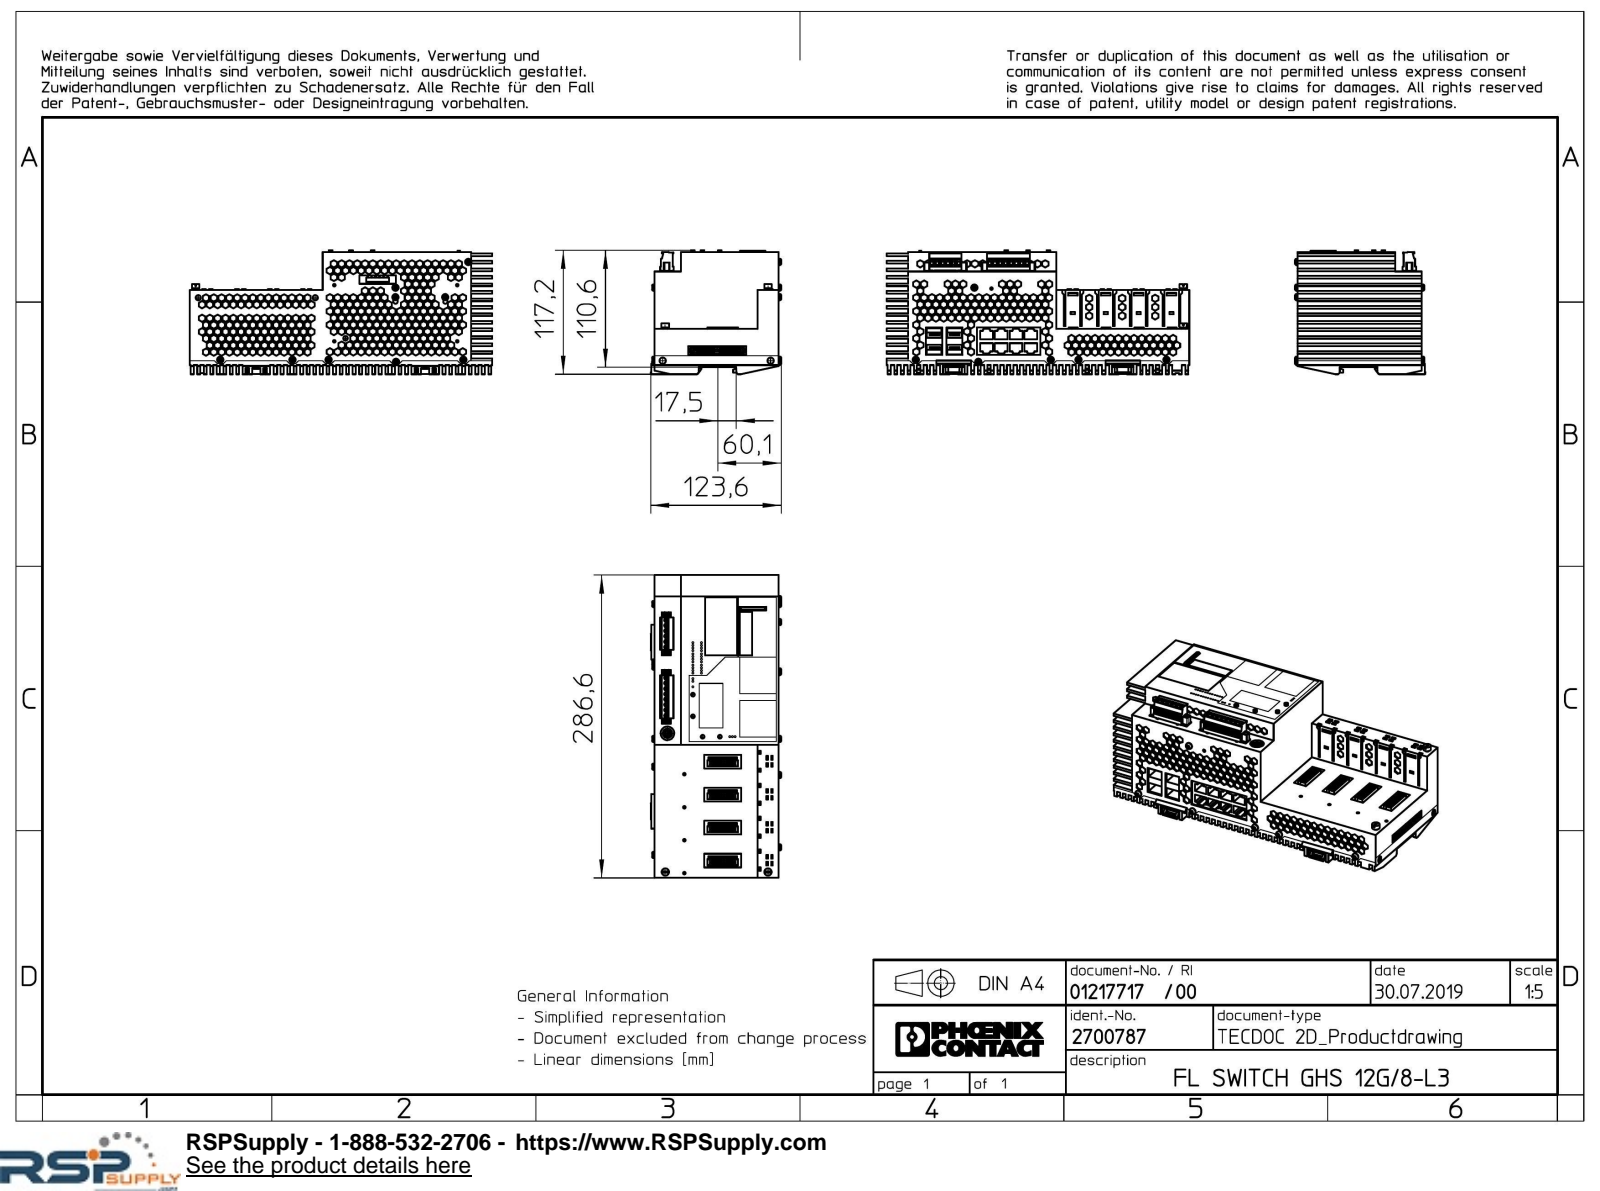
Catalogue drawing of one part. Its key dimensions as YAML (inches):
part_name: "FL_SWITCH_GHS_12G_8_L3-select"
step_written_by: "Creo Elements/Direct Modeling 20.1A 29-Sep-2018 (C) Parametric Technology GmbH (AUTOMOTIVE_DESIGN)"
units: inches
bodies: {solids: 1, faces: 6620, planar: 6229, cylindrical: 361, other: 30}
overall_size: [11.283, 4.868, 4.614]
volume: 149.1
surface_area: 480.4
round_holes:
  - {diameter: 0.157, count: 14}
  - {diameter: 0.031, count: 6}
  - {diameter: 0.098, count: 5}
  - {diameter: 0.097, count: 4}
  - {diameter: 0.154, count: 4}
  - {diameter: 0.14, count: 2}
  - {diameter: 0.197, count: 2}
  - {diameter: 0.236, count: 2}
  - {diameter: 0.177, count: 1}
  - {diameter: 0.354, count: 1}
  - {diameter: 0.512, count: 1}
round_bosses_or_shafts:
  - {diameter: 0.149, count: 14}
  - {diameter: 0.236, count: 13}
  - {diameter: 0.15, count: 6}
  - {diameter: 0.138, count: 4}
  - {diameter: 0.098, count: 4}
  - {diameter: 0.276, count: 3}
  - {diameter: 0.11, count: 1}
partial_cylinders:
  - {radius: 0.01, count: 28}
  - {radius: 0.115, count: 14}
  - {radius: 0.118, count: 14}
  - {radius: 0.055, count: 13}
  - {radius: 0.012, count: 9}
  - {radius: 0.039, count: 8}
  - {radius: 0.079, count: 4}
  - {radius: 0.087, count: 2}
face_to_face_distances: [0.28, 0.559, 0.839, 0.039, 4.591, 0.181, 0.098, 0.378, 0.461, 1.118]
hole_center_spacings: [0.2, 0.4, 0.6, 2.15, 2.35, 2.55, 1.95, 2.75]
